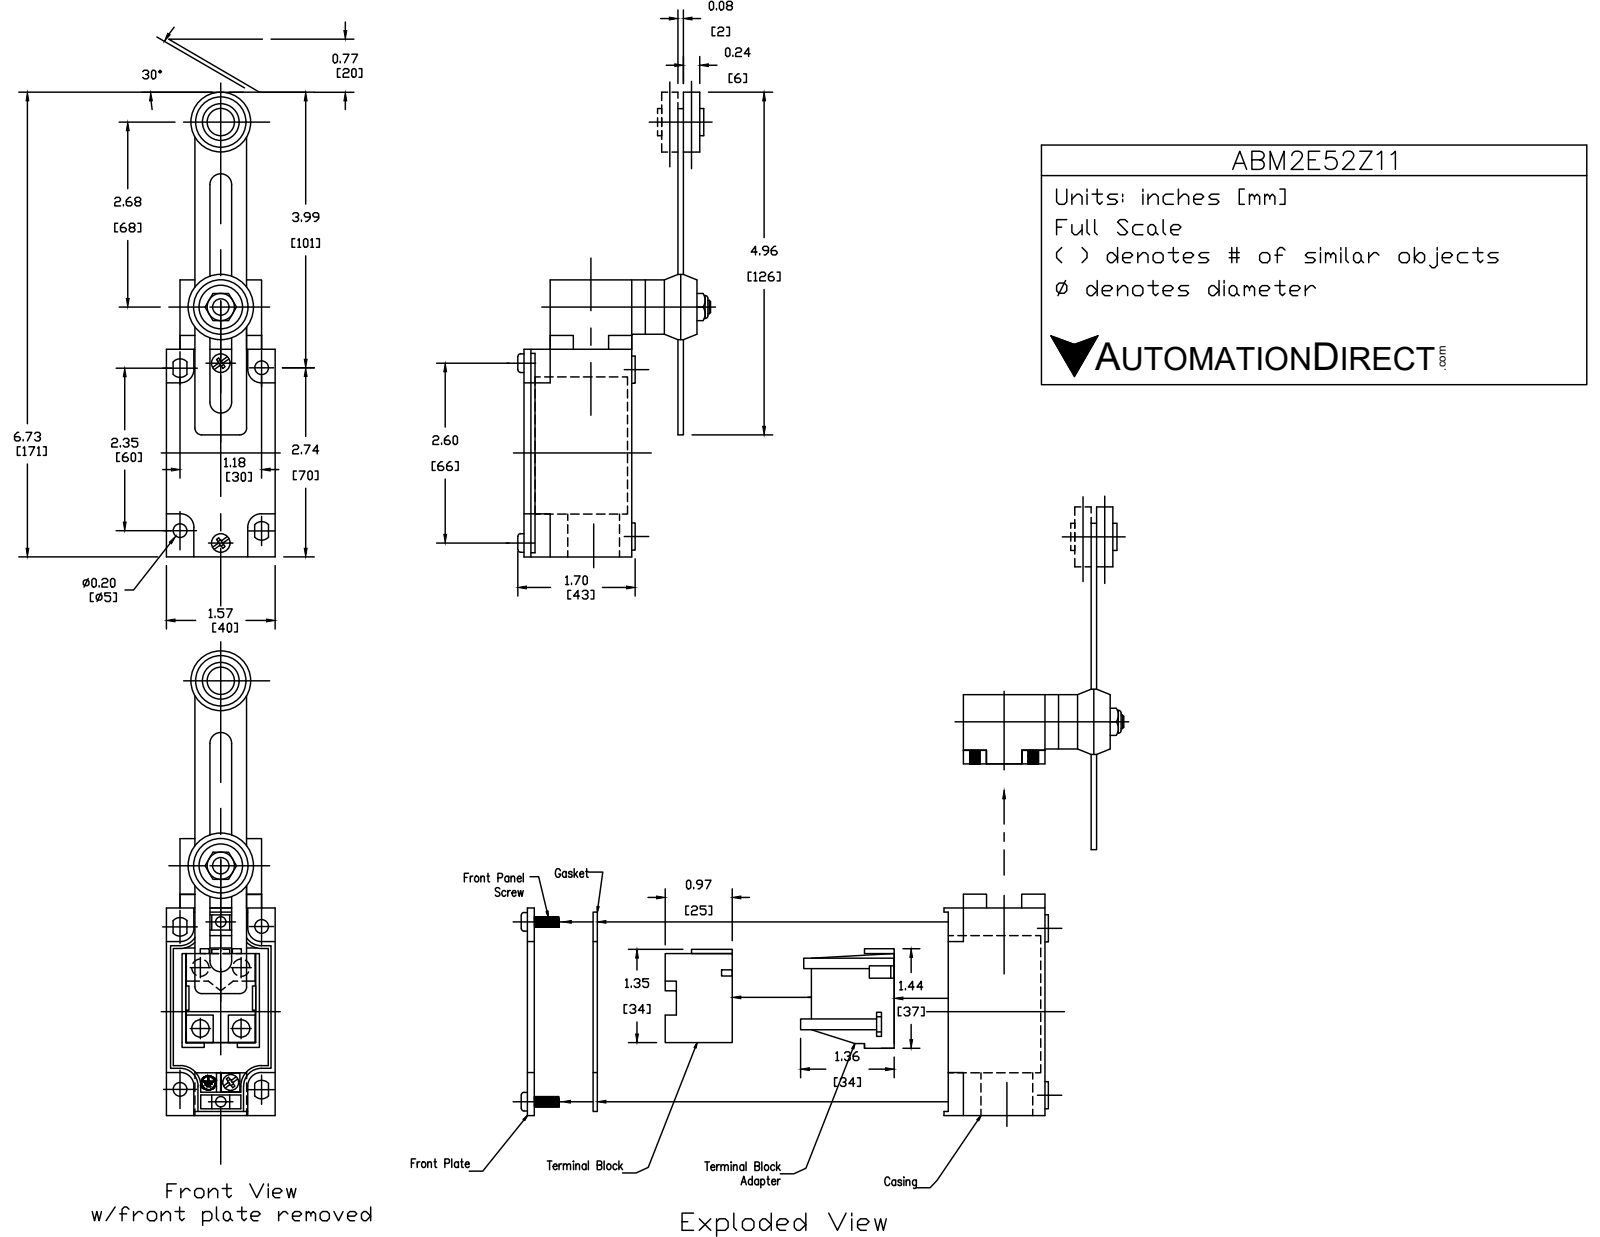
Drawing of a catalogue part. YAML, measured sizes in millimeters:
part_name: "ABM2E52Z11"
step_written_by: "SolidWorks 2017 (AUTOMOTIVE_DESIGN)"
units: millimeters
bodies: {solids: 5, faces: 277, planar: 131, cylindrical: 109, other: 37}
overall_size: [166, 59.7, 40]
volume: 145500
surface_area: 32950
round_holes:
  - {diameter: 5.2, count: 2}
  - {diameter: 3, count: 1}
  - {diameter: 6, count: 1}
  - {diameter: 14, count: 1}
  - {diameter: 17, count: 1}
  - {diameter: 19, count: 1}
round_bosses_or_shafts:
  - {diameter: 10, count: 6}
  - {diameter: 7, count: 3}
  - {diameter: 24, count: 1}
  - {diameter: 22, count: 1}
  - {diameter: 20, count: 1}
  - {diameter: 11.5, count: 1}
  - {diameter: 6, count: 1}
partial_cylinders:
  - {radius: 1.5, count: 16}
  - {radius: 1, count: 4}
  - {radius: 5, count: 4}
  - {radius: 3, count: 2}
  - {radius: 3.3, count: 2}
  - {radius: 4, count: 2}
  - {radius: 7, count: 1}
  - {radius: 11.5, count: 1}
face_to_face_distances: [40, 39.5, 5, 30, 2, 8.2, 47.7, 10.2, 49.7, 35]
hole_center_spacings: [14, 26.6, 67.1, 83.4]
